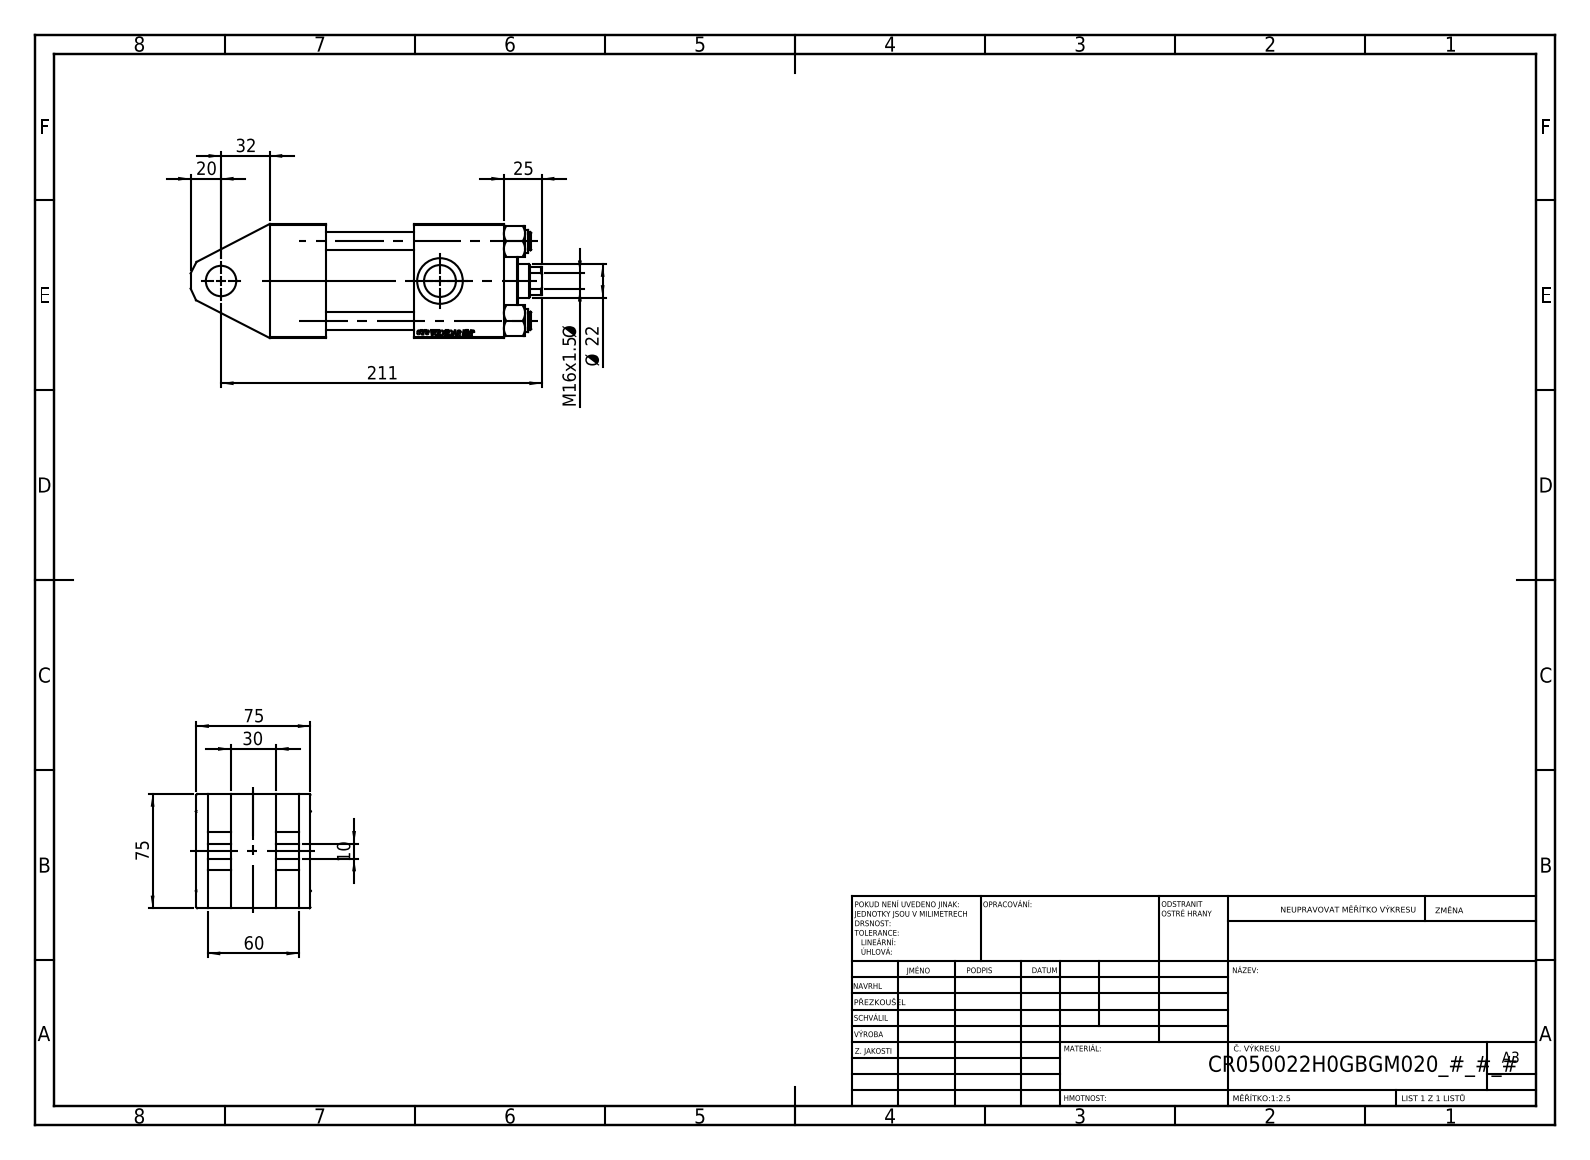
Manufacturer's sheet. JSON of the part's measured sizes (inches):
{"part_name": "V215_VC_A; NUT_M5_H; V215CR_VCP_H; V215CR_TYCINKA_H (+1 more)", "step_written_by": "SolidWorks 2019 (CONFIG_CONTROL_DESIGN)", "units": "inches", "bodies": {"solids": 11, "faces": 1129, "planar": 518, "cylindrical": 83, "other": 528}, "overall_size": [9.094, 2.974, 2.953], "volume_in3": 44.8, "surface_area_in2": 252.4, "round_holes": [[0.472, 4], [0.276, 2], [0.825, 2], [1.181, 2], [0.413, 1], [0.787, 1], [0.866, 1], [0.984, 1], [1.614, 1], [1.969, 1], [2.087, 1]], "round_bosses_or_shafts": [[0.591, 4], [2.205, 1], [1.339, 1]], "partial_cylinders_radius": [[0.413, 1]], "face_to_face_distances": [2.953, 4.606, 2.657, 0.295, 1.772, 0.886, 2.067, 0.591, 3.74, 1.457], "hole_center_spacings": [1.456, 2.059, 2.912, 1.988, 3.681, 5.669]}
